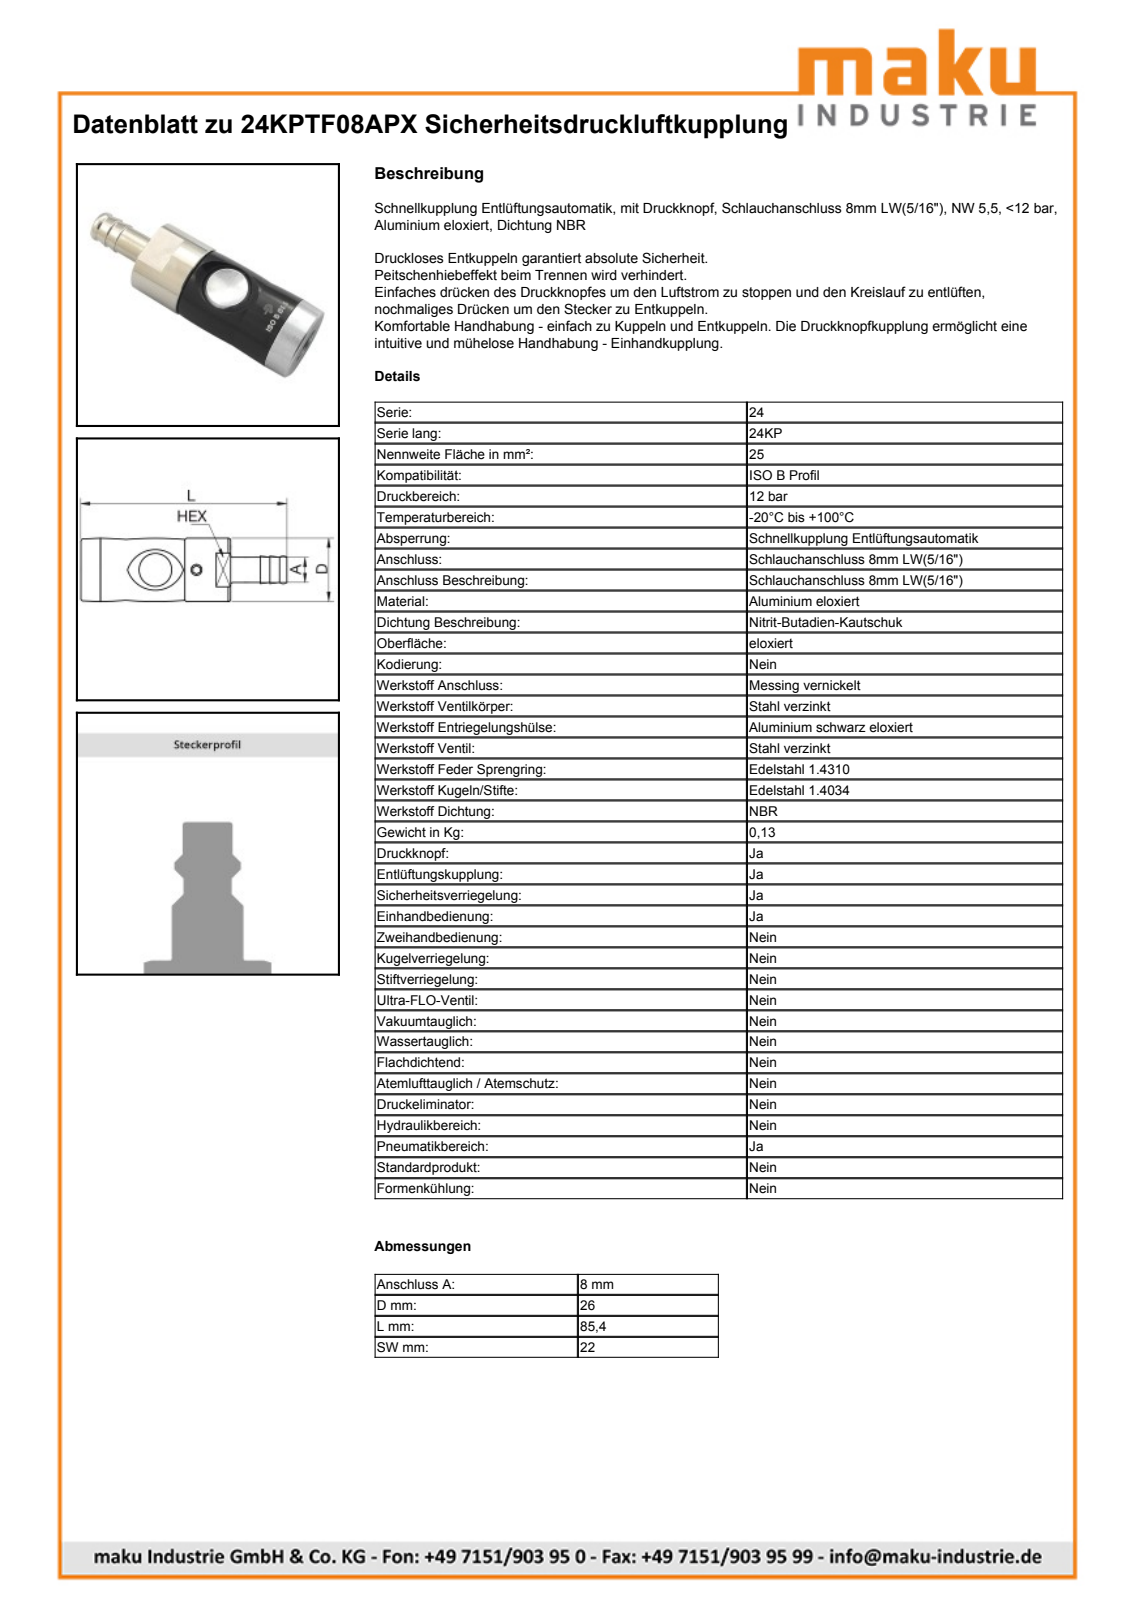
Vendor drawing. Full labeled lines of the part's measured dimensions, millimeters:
Part name (STEP PRODUCT): 24KPTF08APX
STEP written by: Autodesk Inventor 2019 (CONFIG_CONTROL_DESIGN)
Units: millimetres
Bodies: 39 solids, 218 faces (62 planar, 67 cylindrical, 89 other)
Overall size (bounding box): 85.4 × 26 × 26
Volume: 38 732 mm³ · Surface area: 24 206 mm²
Round holes (diameter × count): ⌀12.4 ×2, ⌀3.5 ×1, ⌀6 ×1, ⌀6.5 ×1, ⌀9.6 ×1, ⌀9.65 ×1, ⌀10.6 ×1, ⌀12 ×1, ⌀12.25 ×1, ⌀13.6 ×1, ⌀15 ×1, ⌀15.91 ×1
Round bosses / shafts (diameter × count): ⌀26 ×1, ⌀22.42 ×1, ⌀22 ×1, ⌀20.5 ×1, ⌀18.1 ×1, ⌀16.5 ×1, ⌀16.4 ×1, ⌀15.8 ×1
Partial cylindrical surfaces — rounded edges, fillets, slot ends (radius × count): R6.2 ×2
Main face-to-face distances: 43.1, 19, 62.1, 54, 35, 8.1, 1, 61.1, 42.1, 7.1
Hole centre spacings: 0.6, 0.7, 1.3, 17.05
